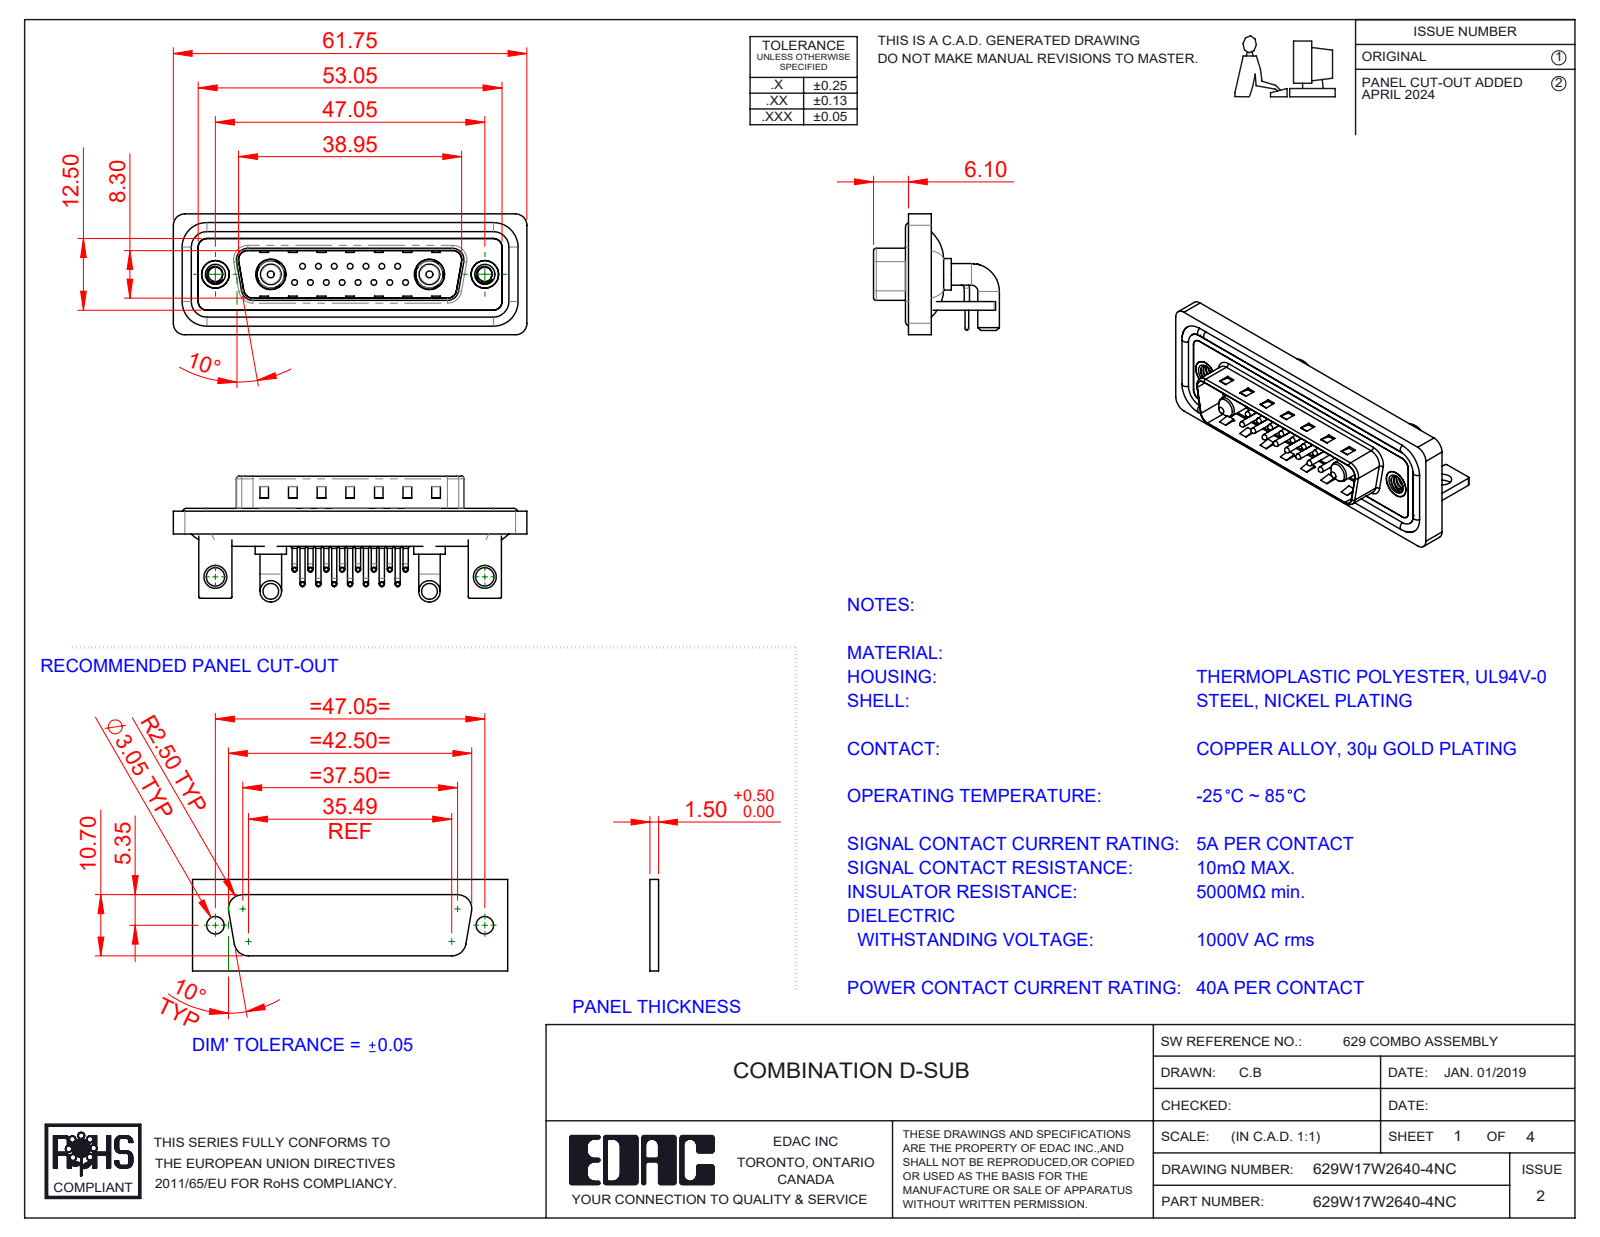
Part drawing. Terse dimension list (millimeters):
name: 629Combo Contact Row 1; 629Combo Shell Rear_25 Contacts; Power Pin_40A RA; 629Combo Shell Front_25 Contacts (+6 more)
written by: SolidWorks 2023 (CONFIG_CONTROL_DESIGN)
unit: mm
bodies: 28 solids, 2257 faces (1209 planar, 788 cylindrical, 260 other)
size: 61.75 × 21.98 × 21.1
volume: 7 930 mm³; area: 13 277 mm²
holes: 15× ⌀0.75, 15× ⌀1.6, 15× ⌀2, 2× ⌀2.5, 2× ⌀3.2, 2× ⌀4, 2× ⌀4.8, 2× ⌀4.85, 2× ⌀5, 2× ⌀5.3
bosses: 30× ⌀0.9, 15× ⌀1.5, 15× ⌀1, 15× ⌀0.65, 4× ⌀3.75, 4× ⌀1.6, 2× ⌀5.5, 2× ⌀5.2
rounds: 19× R2, 18× R1.5, 16× R0.25, 15× R1.01, 9× R0.5, 8× R1.6, 4× R0.6, 4× R0.65
face distances: 0.4, 0.8, 2.1, 1.5, 2.9, 1.1, 4.1, 1.6, 4.5, 3.7
hole spacings: 3.16, 2.77, 5.54, 8.31, 5.04, 7.49, 11.08, 5.03
